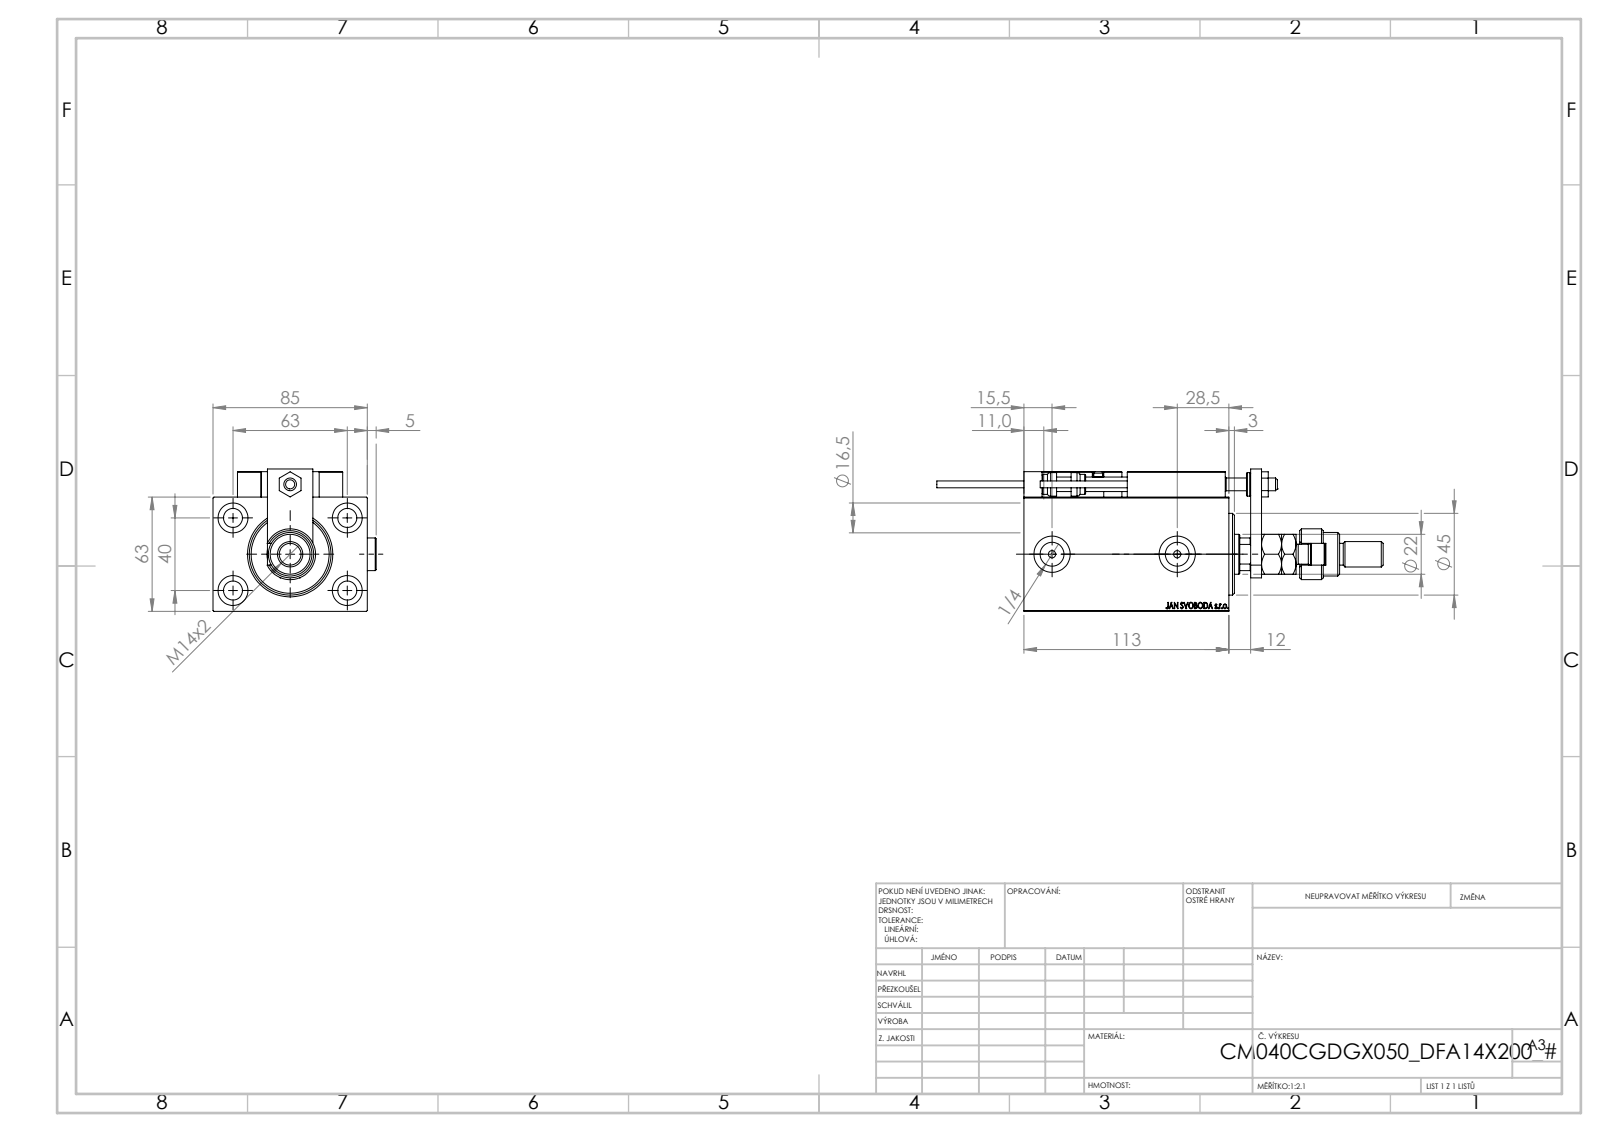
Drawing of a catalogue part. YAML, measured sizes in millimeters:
part_name: "NUT_D12; Zatka_OIL_PORT; FEMALE_PART_FOR_DFA; ALLEN BOLT D5 (+7 more)"
step_written_by: "SolidWorks 2019 (CONFIG_CONTROL_DESIGN)"
units: millimeters
bodies: {solids: 27, faces: 1421, planar: 622, cylindrical: 217, other: 582}
overall_size: [246, 89.9, 78.5]
volume: 582297
surface_area: 128924
round_holes:
  - {diameter: 4, count: 6}
  - {diameter: 8, count: 5}
  - {diameter: 16.5, count: 5}
  - {diameter: 3.2, count: 4}
  - {diameter: 10.5, count: 4}
  - {diameter: 5, count: 2}
  - {diameter: 13.16, count: 2}
  - {diameter: 20, count: 2}
  - {diameter: 7, count: 1}
  - {diameter: 12.5, count: 1}
  - {diameter: 22, count: 1}
  - {diameter: 25.5, count: 1}
round_bosses_or_shafts:
  - {diameter: 18, count: 3}
  - {diameter: 11, count: 2}
  - {diameter: 5, count: 2}
  - {diameter: 3.8, count: 2}
  - {diameter: 28, count: 1}
  - {diameter: 24, count: 1}
  - {diameter: 14, count: 1}
  - {diameter: 13, count: 1}
partial_cylinders:
  - {radius: 0.3, count: 30}
  - {radius: 3, count: 2}
  - {radius: 9.75, count: 1}
  - {radius: 10.5, count: 1}
face_to_face_distances: [63, 85, 12, 101, 113, 14, 6, 30, 18, 77]
hole_center_spacings: [37.31, 11.37, 20, 29.59, 29.69, 36.06, 36.53, 40]
